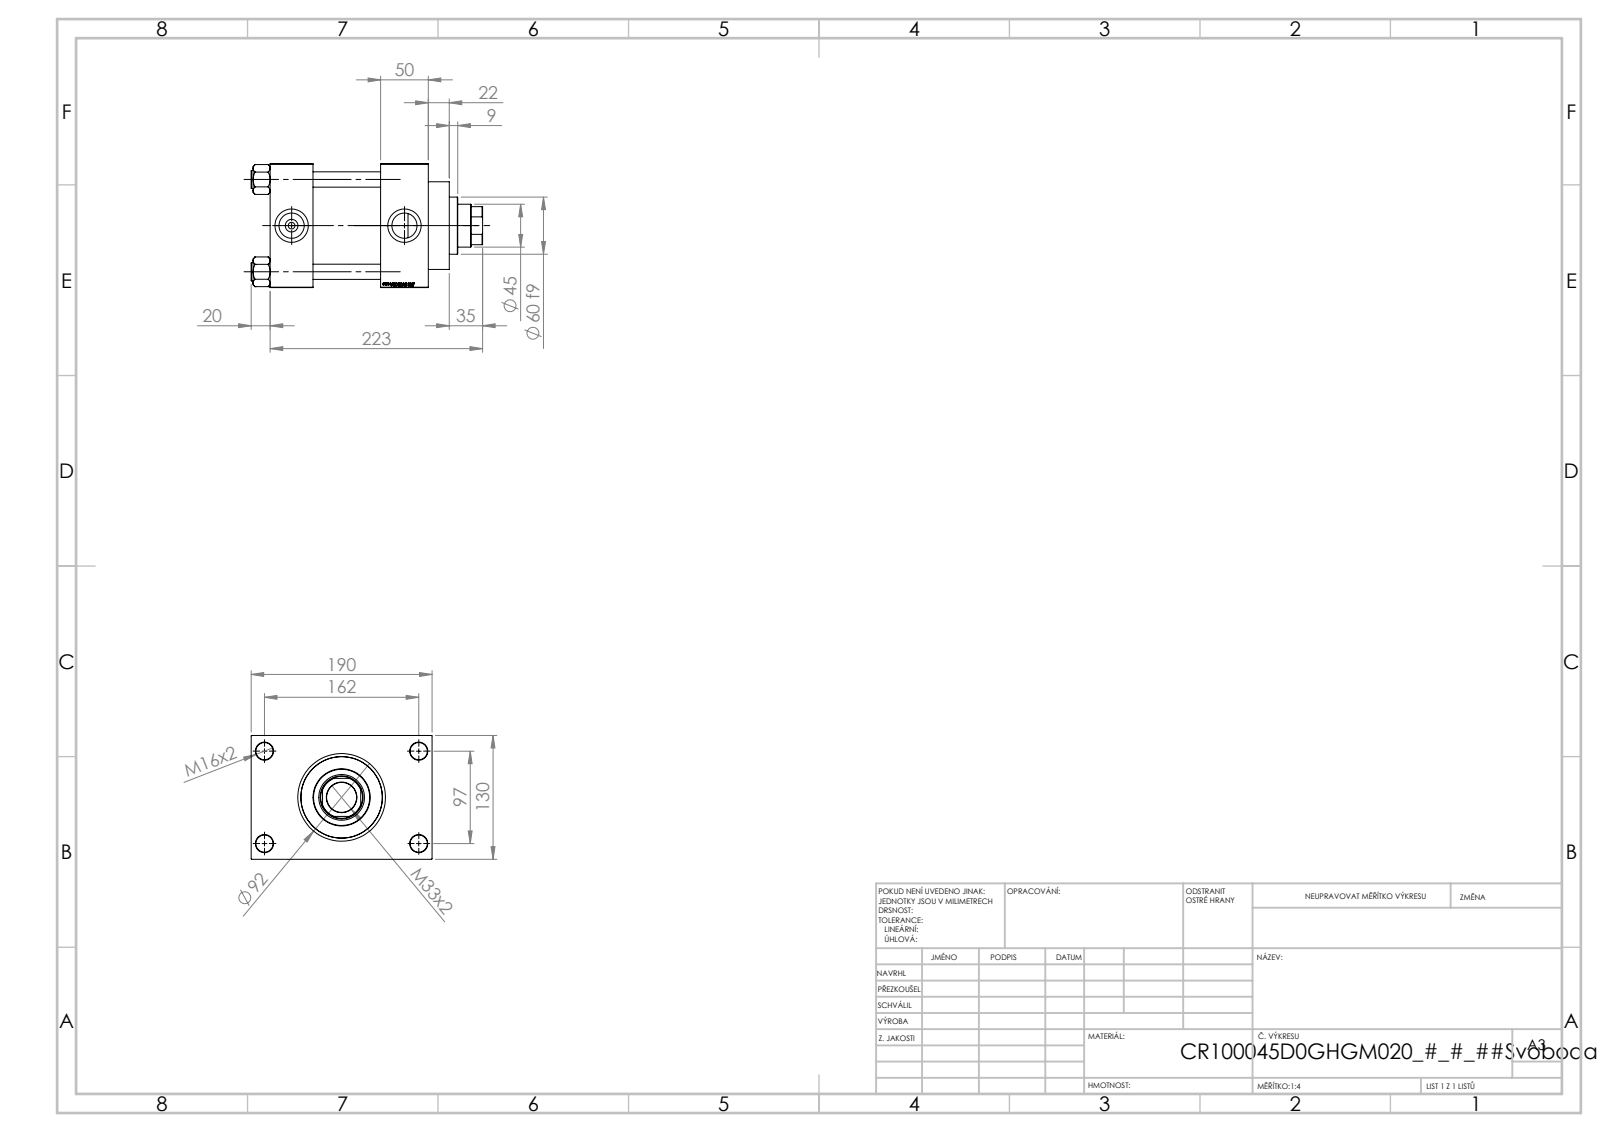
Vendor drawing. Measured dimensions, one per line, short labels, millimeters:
name: V215_VC_A; V215CR_D_TYCINKA; V215CR_VCP_D; NUT_M5_D (+1 more)
written by: SolidWorks 2019 (CONFIG_CONTROL_DESIGN)
unit: mm
bodies: 11 solids, 1151 faces (545 planar, 88 cylindrical, 518 other)
size: 243 × 190 × 130
volume: 2 590 000 mm³; area: 354 877 mm²
holes: 4× ⌀16, 4× ⌀18, 2× ⌀7, 2× ⌀26.44, 2× ⌀35, 1× ⌀31.5, 1× ⌀45, 1× ⌀48, 1× ⌀76, 1× ⌀85.5, 1× ⌀100
bosses: 4× ⌀19, 1× ⌀106, 1× ⌀92, 1× ⌀60
rounds: 1× R22
face distances: 130, 45, 116, 71, 166, 121, 50, 30, 160, 20
hole spacings: 32.55, 68.52, 94.41, 96.9, 102.27, 129.45, 161.73, 97
